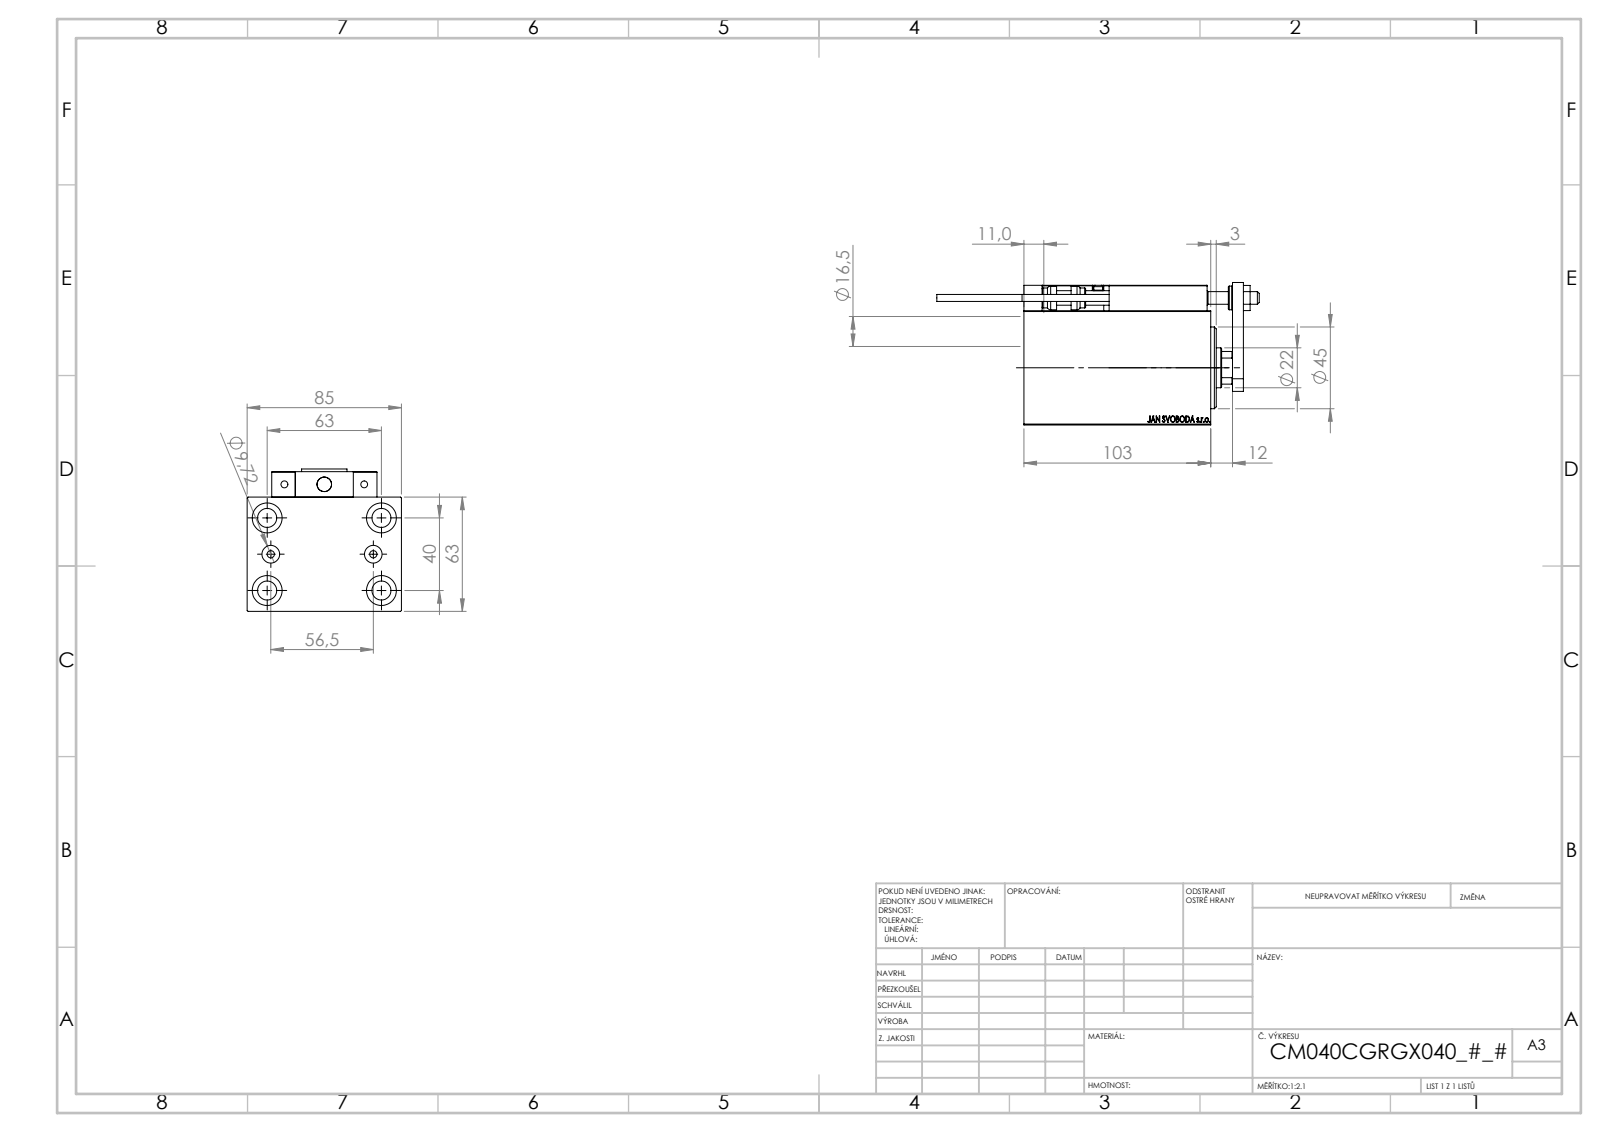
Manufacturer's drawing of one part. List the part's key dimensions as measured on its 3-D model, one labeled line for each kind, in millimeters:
Part name (STEP PRODUCT): SWITCH DIM B,W; ZARAZKA; NUT_D12; SWITCH_X_FRONT_BACK (+8 more)
STEP written by: SolidWorks 2019 (CONFIG_CONTROL_DESIGN)
Units: millimetres
Bodies: 23 solids, 1278 faces (560 planar, 184 cylindrical, 534 other)
Overall size (bounding box): 177.7 × 85 × 78.5
Volume: 520 217 mm³ · Surface area: 113 103 mm²
Round holes (diameter × count): ⌀4 ×6, ⌀8 ×5, ⌀16.5 ×5, ⌀3.2 ×4, ⌀10.5 ×4, ⌀5 ×2, ⌀9.72 ×2, ⌀7 ×1, ⌀12.5 ×1, ⌀22 ×1, ⌀25.5 ×1, ⌀40 ×1
Round bosses / shafts (diameter × count): ⌀5 ×2, ⌀3.8 ×2, ⌀13 ×1, ⌀11 ×1
Partial cylindrical surfaces — rounded edges, fillets, slot ends (radius × count): R0.3 ×30, R3 ×2, R10.5 ×1
Main face-to-face distances: 63, 85, 12, 91, 103, 14, 77, 15, 18, 30
Hole centre spacings: 37.31, 11.37, 20, 20.1, 20.5, 29.59, 29.69, 36.06
